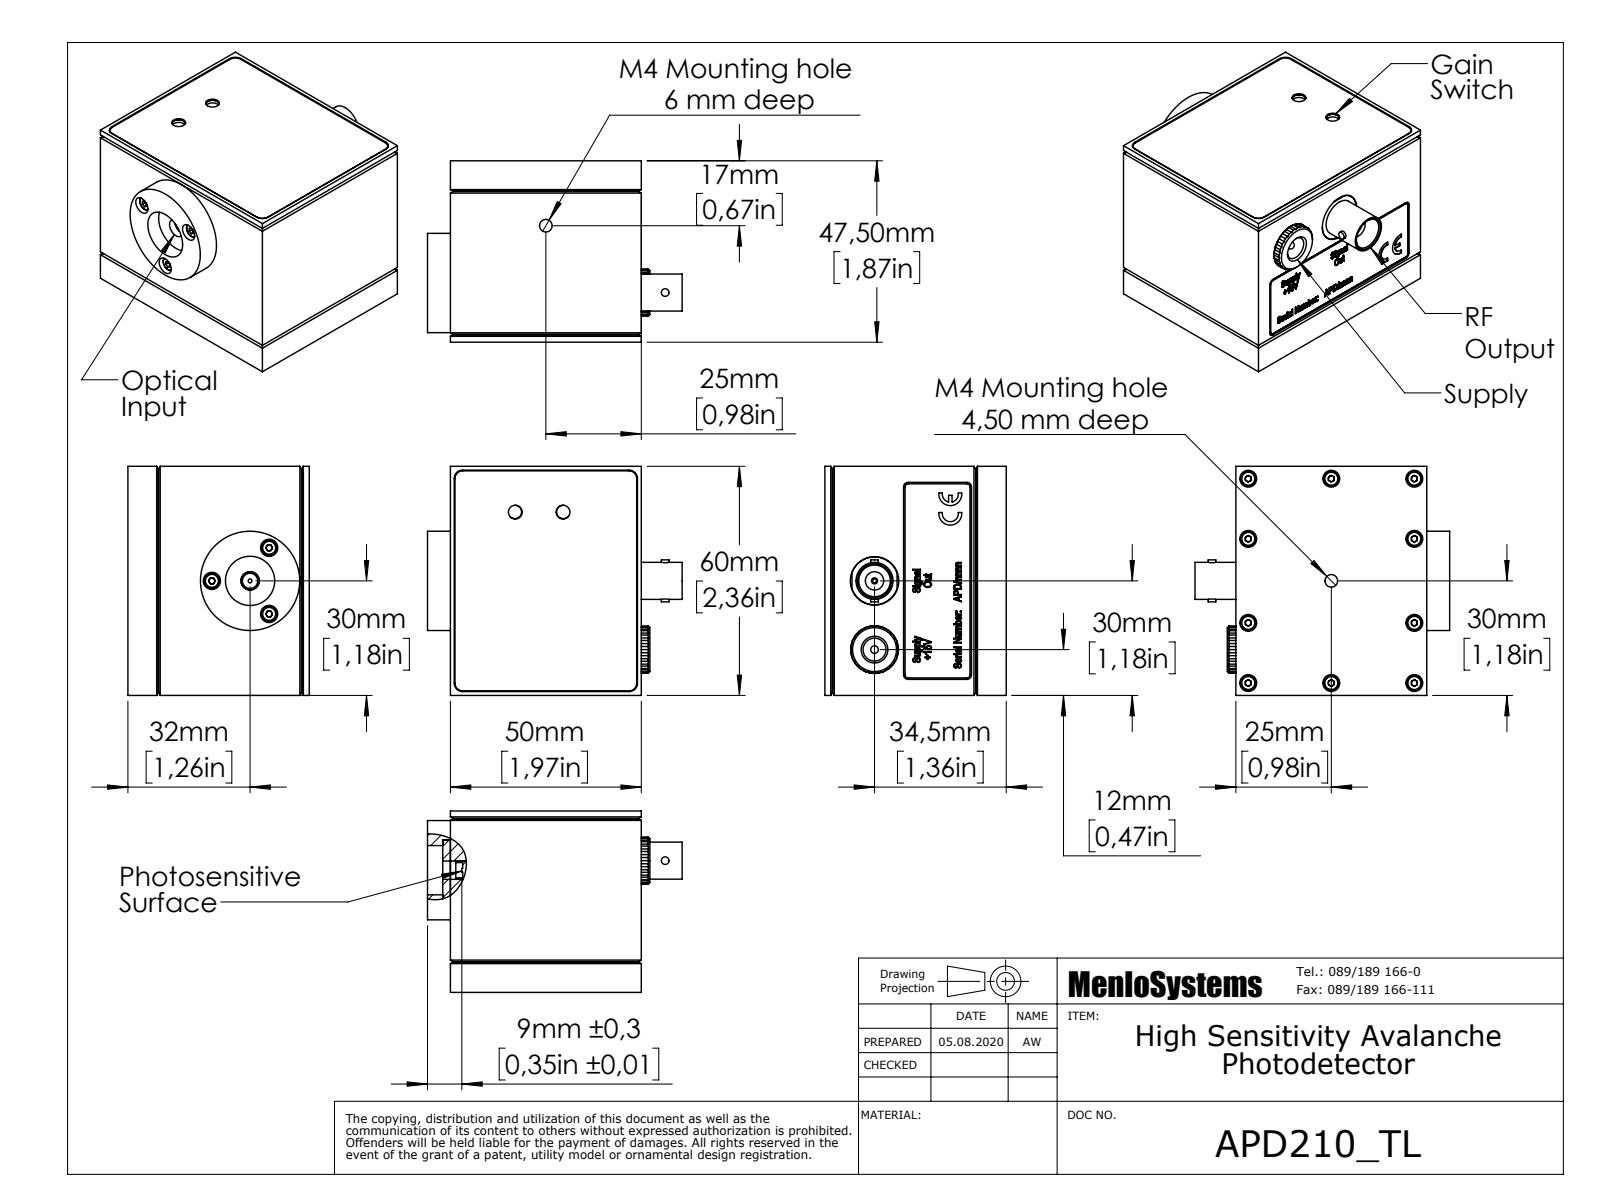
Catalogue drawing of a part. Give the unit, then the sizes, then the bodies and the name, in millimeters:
Units: millimetres
Overall size (bounding box): 66.7 × 60 × 47.5
Round holes (diameter × count): ⌀1.6 ×27, ⌀4 ×11, ⌀2.2 ×10, ⌀2.4 ×10, ⌀4.4 ×10, ⌀2.1 ×3, ⌀4.5 ×3, ⌀3.3 ×2, ⌀3.6 ×2, ⌀4.2 ×2, ⌀5 ×2, ⌀8.74 ×2
Round bosses / shafts (diameter × count): ⌀2 ×15, ⌀3.8 ×13, ⌀0.5 ×3, ⌀8.71 ×2, ⌀8.21 ×2, ⌀7.37 ×2, ⌀26 ×1, ⌀15.72 ×1
Partial cylindrical surfaces — rounded edges, fillets, slot ends (radius × count): R3 ×10, R2.5 ×6, R0.8 ×4, R1.2 ×4, R2 ×4, R2.2 ×4, R0.85 ×2, R2.1 ×2
Main face-to-face distances: 45, 5, 0.35, 1.5, 11.5, 0.5, 47.05, 47.4, 45.5, 8
Hole centre spacings: 15.5, 15.75, 21.5, 21.75, 22, 37.5, 37.75, 43.25
Volume: 77 159 mm³ · Surface area: 51 063 mm²
Bodies: 25 solids, 1515 faces (719 planar, 352 cylindrical, 444 other)
Part name (STEP PRODUCT): APD210_2020805
STEP written by: SolidWorks 2018 (AUTOMOTIVE_DESIGN)
